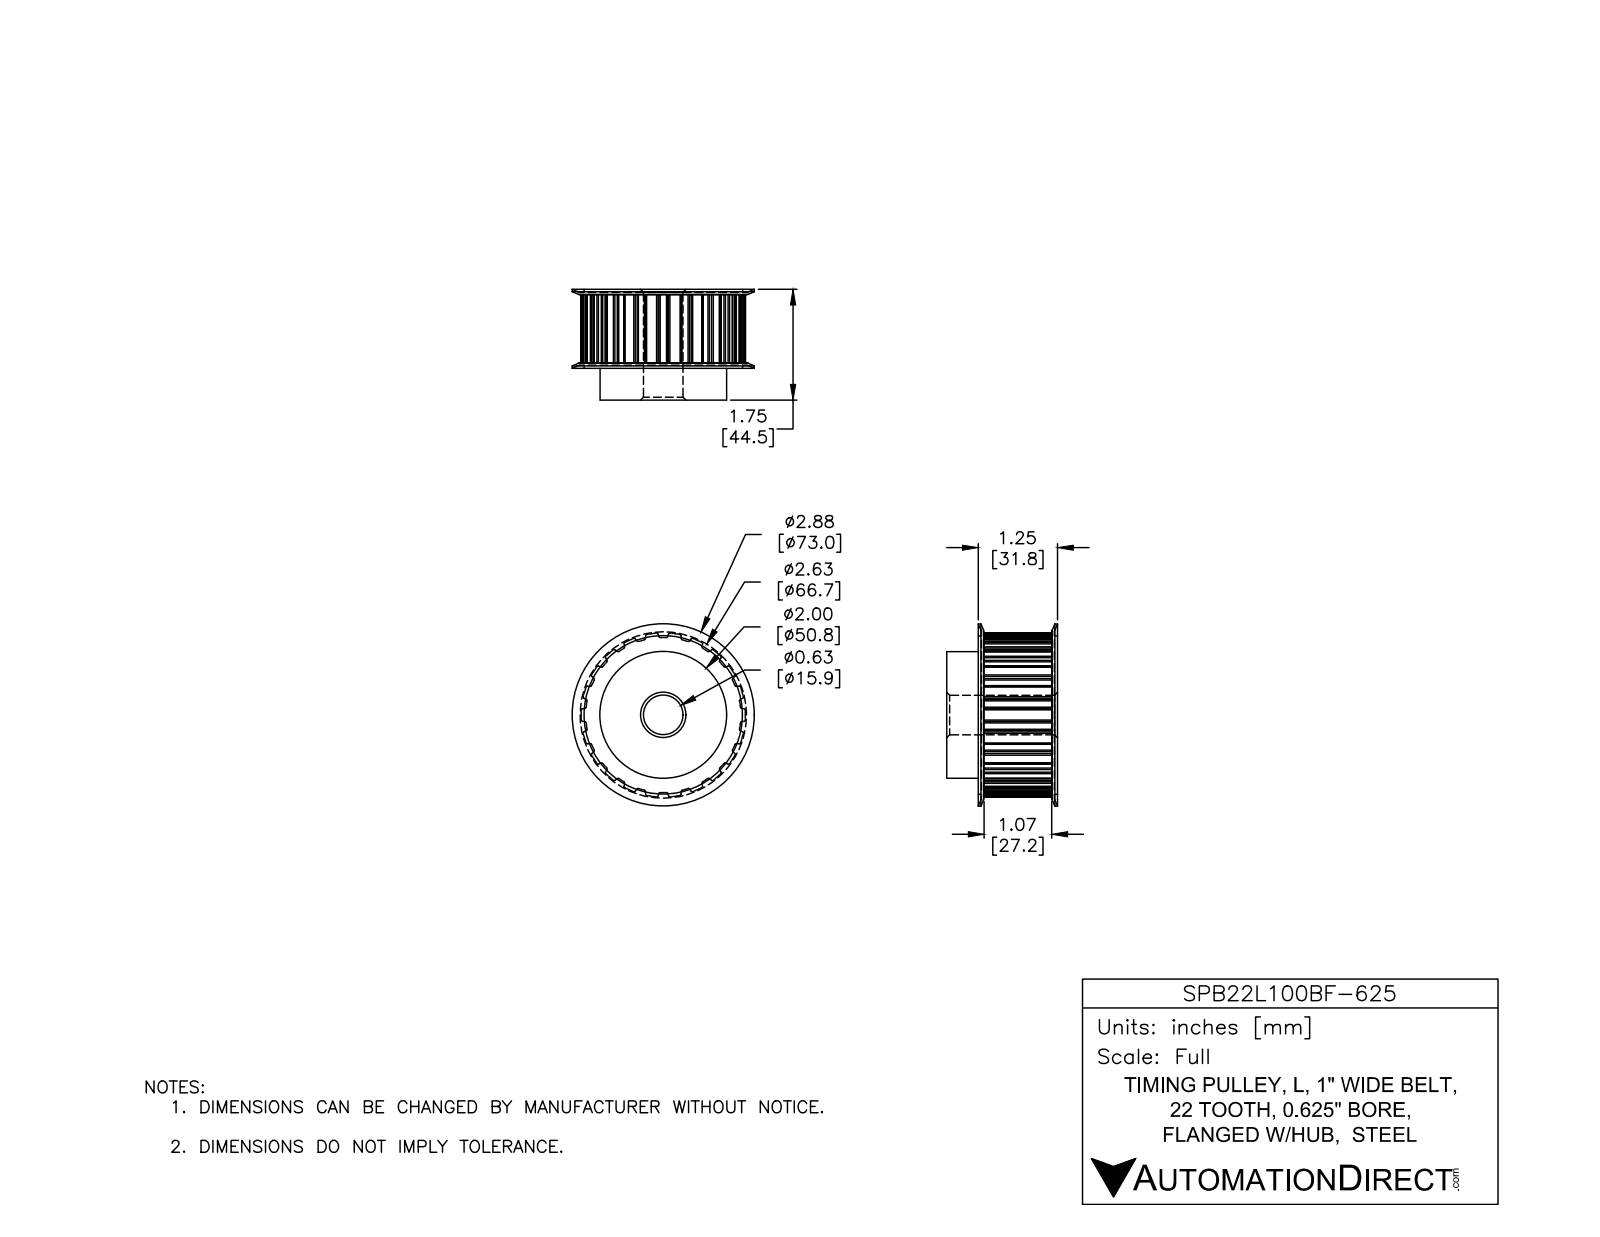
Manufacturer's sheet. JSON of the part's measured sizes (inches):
{"part_name": "SPB22L100BF-625", "step_written_by": "SolidWorks 2015 (AUTOMOTIVE_DESIGN)", "units": "inches", "bodies": {"solids": 1, "faces": 228, "planar": 73, "cylindrical": 139, "other": 16}, "overall_size": [2.875, 2.875, 1.75], "volume_in3": 7.433, "surface_area_in2": 34.33, "round_holes": [[0.625, 1]], "round_bosses_or_shafts": [[2.875, 1], [2.875, 1], [2.501, 1], [2, 1]], "partial_cylinders_radius": [[0.02, 88], [1.298, 1]], "face_to_face_distances": [1.75, 1.25, 0.5, 0.05, 1.2, 2.446, 0.09, 1.16, 0.04, 1.11]}
